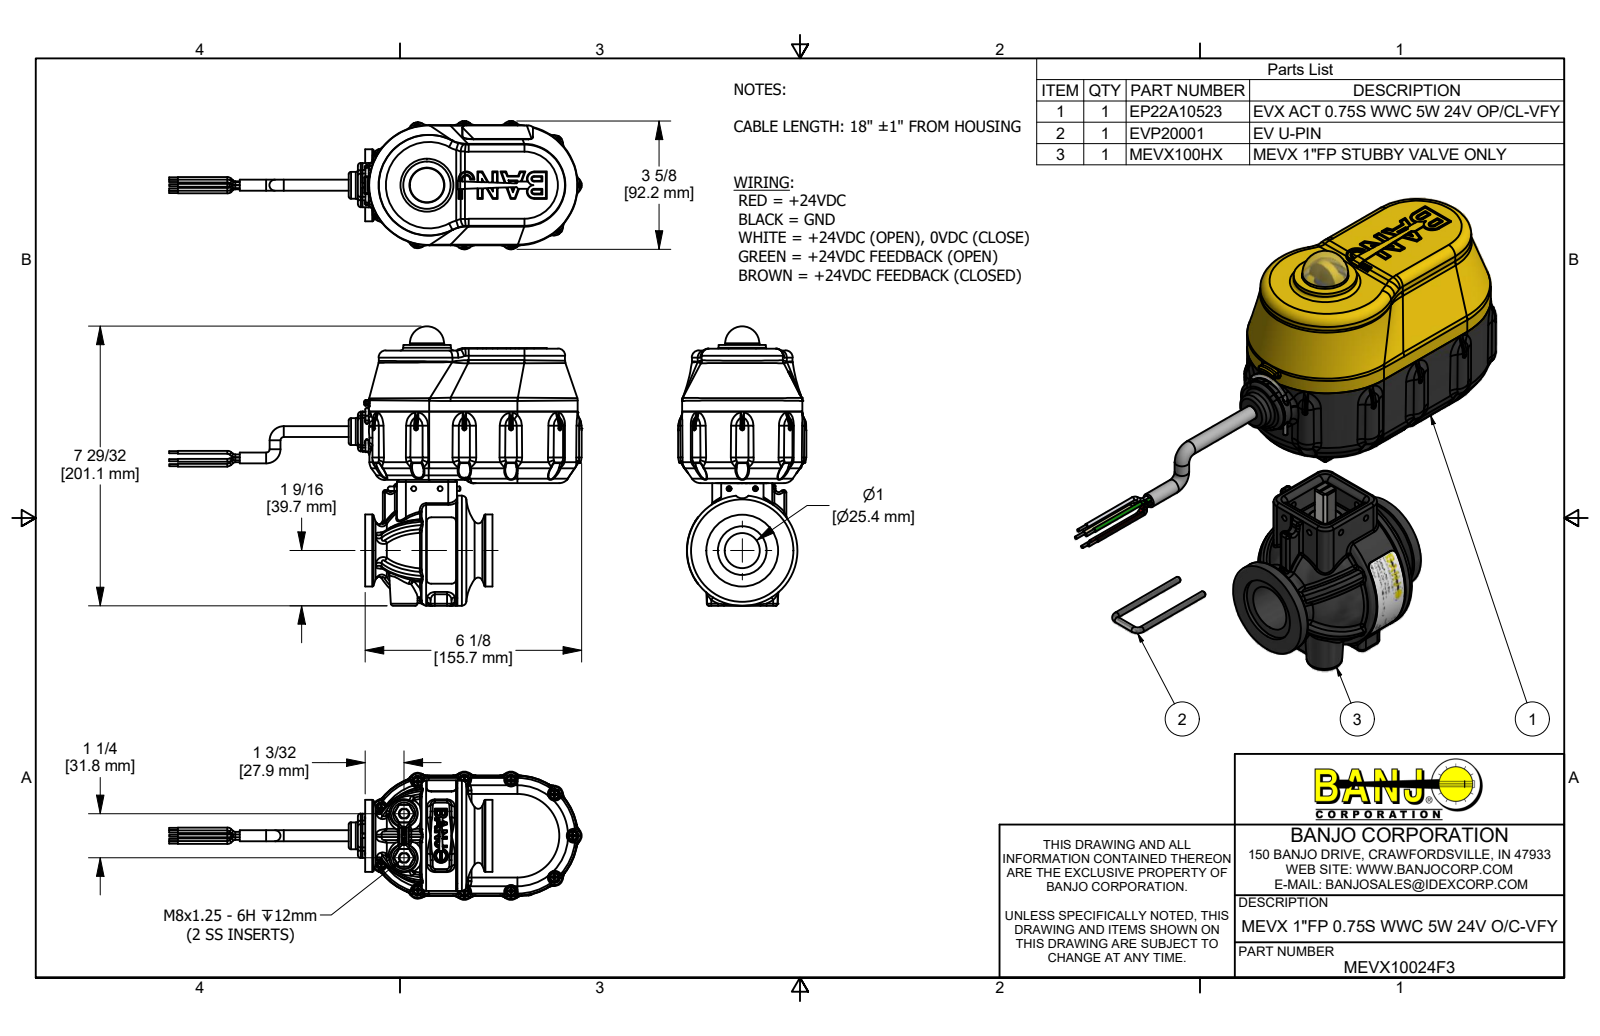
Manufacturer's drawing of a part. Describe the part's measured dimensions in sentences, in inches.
The part is named "MEVX10024F3; EP22A10523; B61905PPHS; B632038PM (+8 more)". Its 3-D file was written by "Autodesk Inventor 2019 (AUTOMOTIVE_DESIGN)". It is 84 solids with 10990 faces: 2994 planar, 3118 cylindrical and 4878 other. Overall it measures 11.685 by 7.916 by 3.63 inches. Its volume is 46.48 cubic inches and its surface area 533 square inches. Round holes: 11 of diameter 0.095, 11 of diameter 0.15, 7 of diameter 0.08, 5 of diameter 0.135, 4 of diameter 0.107, 4 of diameter 0.126, 4 of diameter 0.136, 4 of diameter 0.148, 4 of diameter 0.15, 4 of diameter 0.17, 2 of diameter 0.105, 2 of diameter 0.118. Round bosses or shafts: 25 of diameter 0.08, 17 of diameter 0.25, 11 of diameter 0.14, 11 of diameter 0.108, 11 of diameter 0.085, 10 of diameter 0.058, 4 of diameter 0.27, 4 of diameter 0.219. Partial cylindrical surfaces (rounded edges, fillets, slot ends): 180 of radius 0.013, 145 of radius 0.04, 84 of radius 0.01, 71 of radius 0.02, 54 of radius 0.005, 46 of radius 0.06, 30 of radius 0.03, 28 of radius 0.08. The main face-to-face distances are 0.1, 2.565, 0.211, 0.06, 0.151, 1.685, 1.836, 1.896, 2.465, 0.78. The hole center spacings are 1.283, 2.69, 2.715, 1.513, 1.662, 1.79, 2.849, 3.789.
